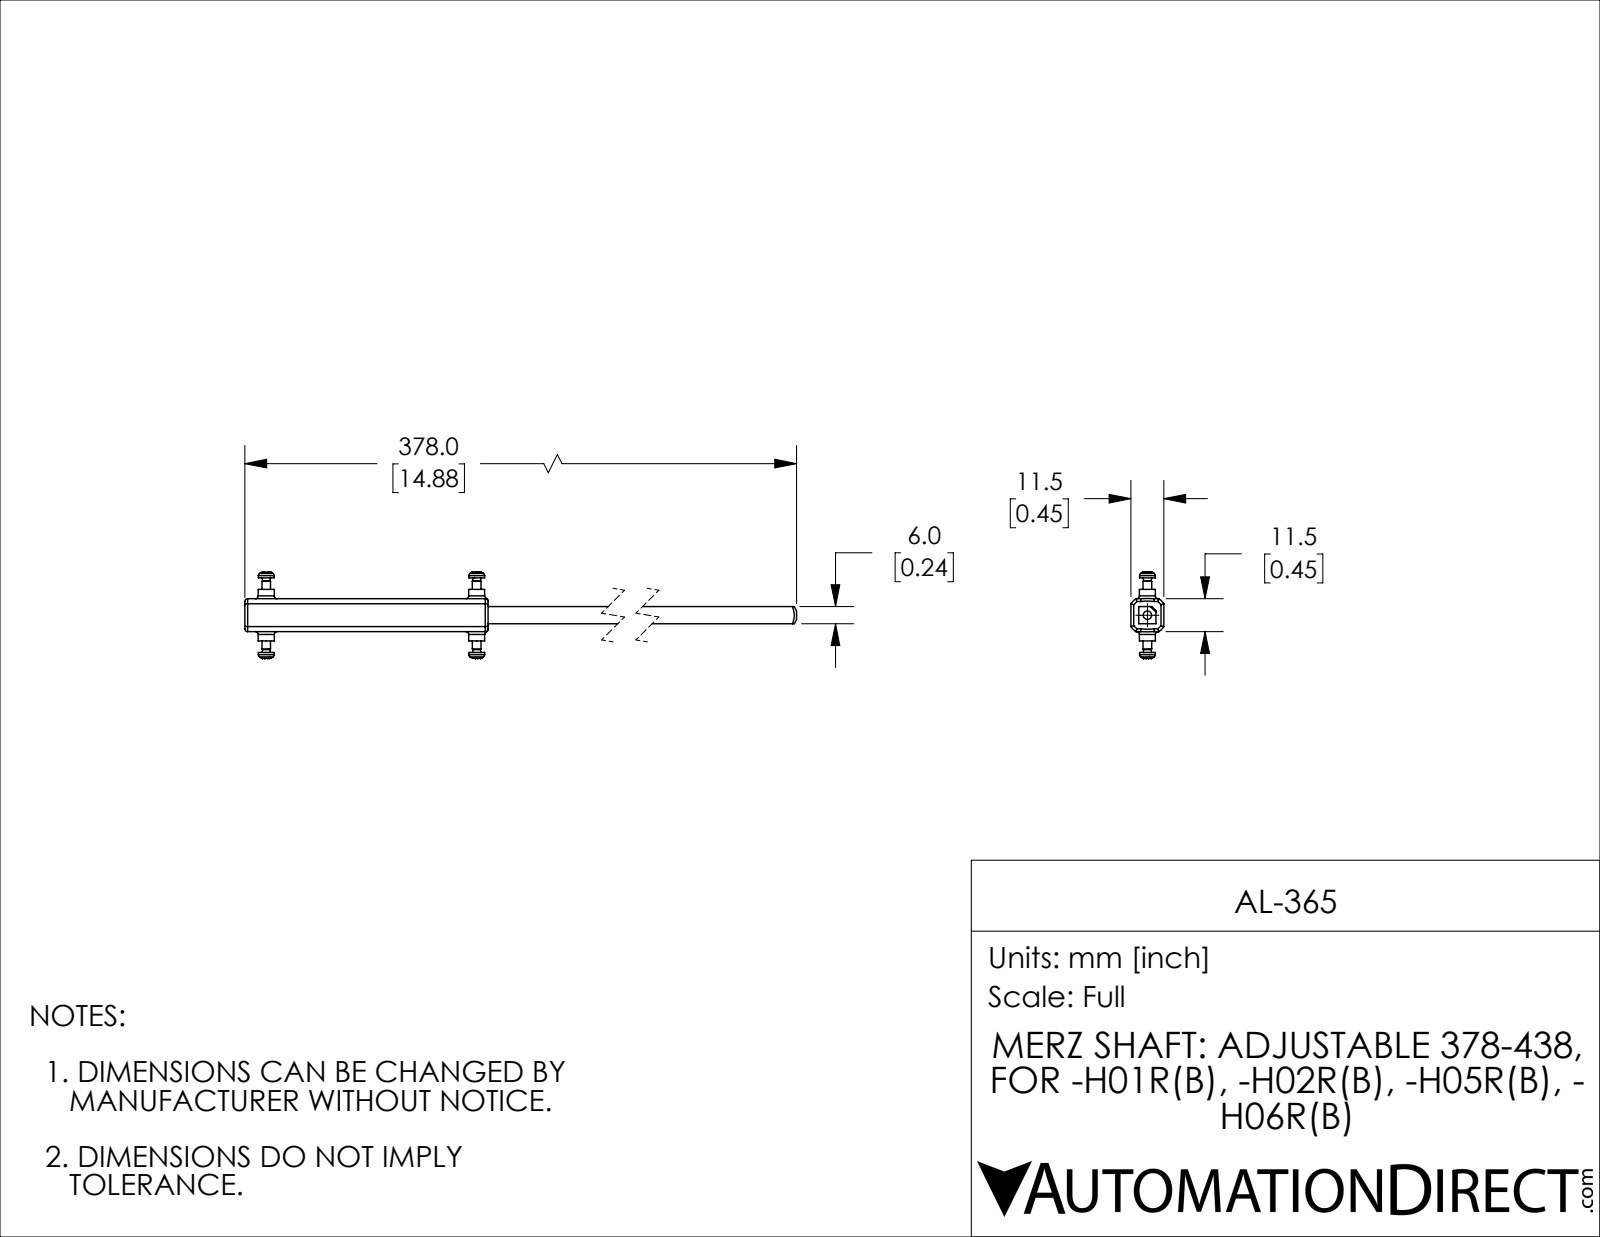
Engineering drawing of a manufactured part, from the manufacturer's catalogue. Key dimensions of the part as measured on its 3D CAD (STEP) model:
Part name (STEP PRODUCT): AL-365
STEP written by: SolidWorks 2019 (AUTOMOTIVE_DESIGN)
Units: inches
Bodies: 6 solids, 211 faces (93 planar, 56 cylindrical, 62 other)
Overall size (bounding box): 14.882 × 1.194 × 0.453
Volume: 1.267 in³ · Surface area: 23.39 in²
Round holes (diameter × count): ⌀0.118 ×3, ⌀0.091 ×2
Round bosses / shafts (diameter × count): ⌀0.22 ×2, ⌀0.217 ×2
Partial cylindrical surfaces — rounded edges, fillets, slot ends (radius × count): R0.039 ×8, R0.276 ×1
Main face-to-face distances: 0.236, 0.108, 0.344, 0.453, 0.016, 0.472, 0.63, 0.157, 0.128, 0.581
Hole centre spacings: 2.894
